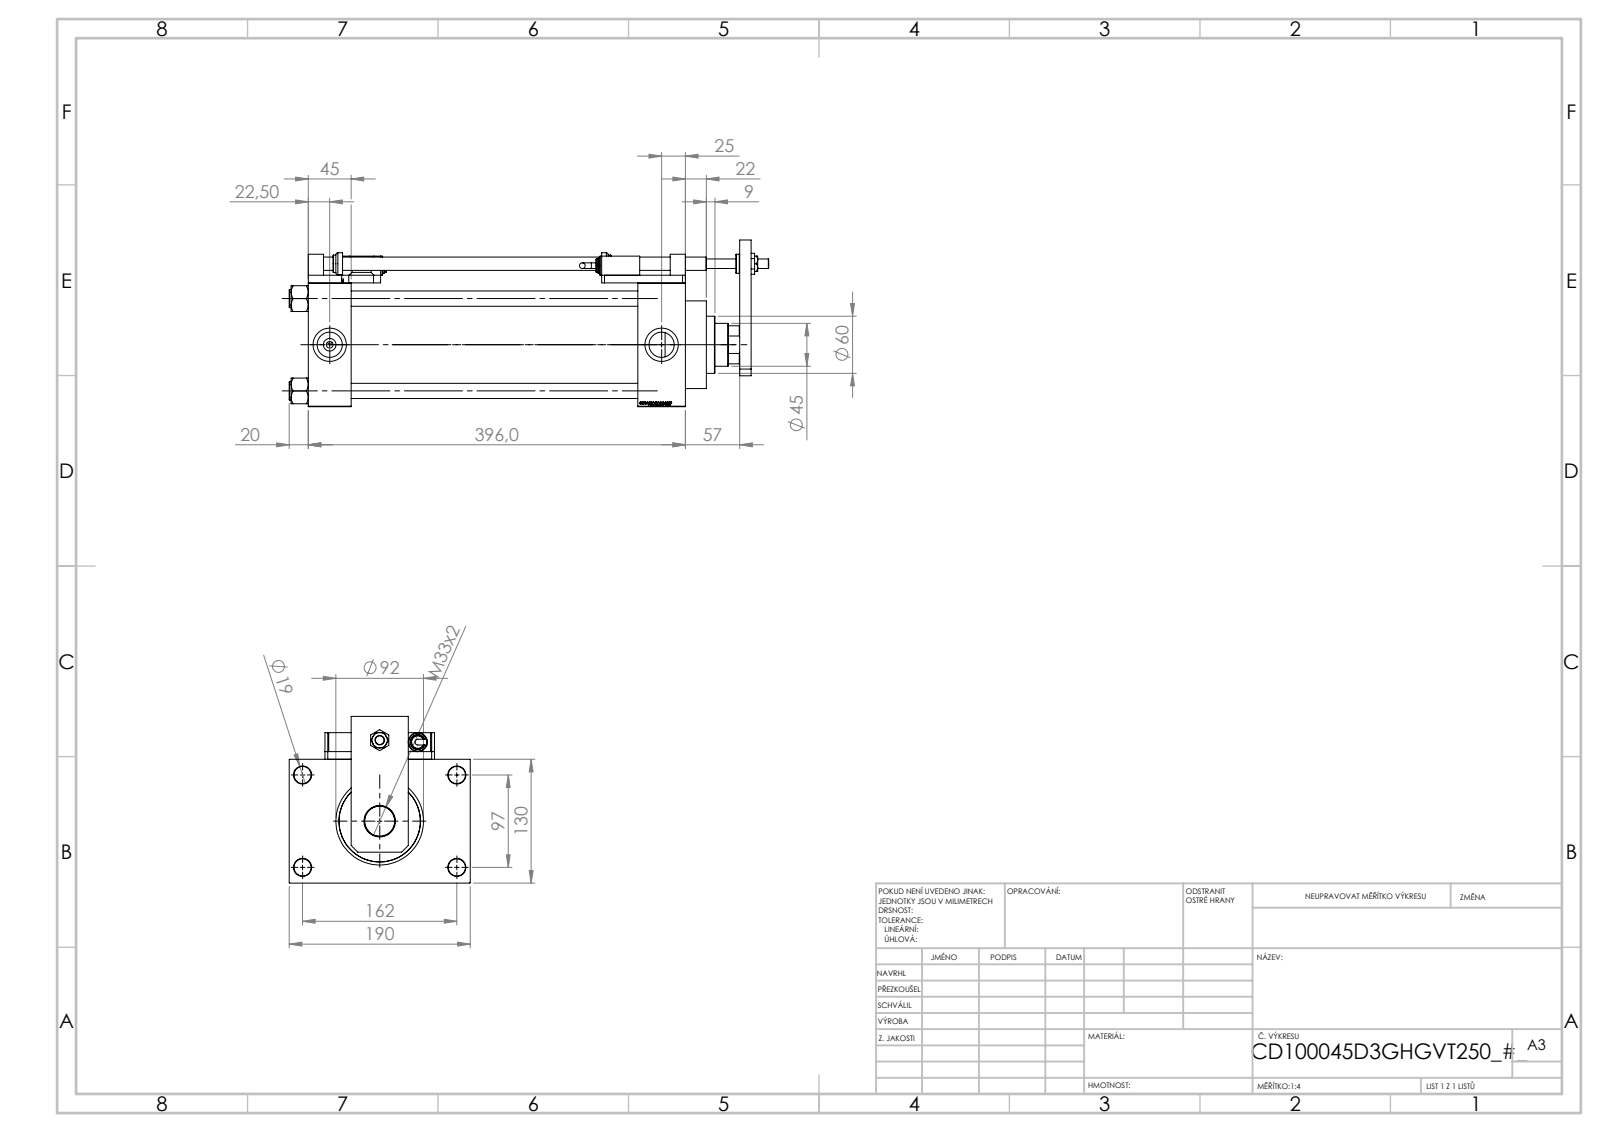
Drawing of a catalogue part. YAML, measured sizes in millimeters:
part_name: "V215CD_SWITCH_Q_SWITCH; V215CD_VC_A; V215CD_NUT_M5_D; Zatka_pro_OIL_PORT (+8 more)"
step_written_by: "SolidWorks 2019 (CONFIG_CONTROL_DESIGN)"
units: millimeters
bodies: {solids: 26, faces: 1480, planar: 714, cylindrical: 167, other: 599}
overall_size: [503.5, 190, 175]
volume: 3715000
surface_area: 696735
round_holes:
  - {diameter: 8.5, count: 4}
  - {diameter: 13.5, count: 4}
  - {diameter: 16, count: 4}
  - {diameter: 18, count: 4}
  - {diameter: 26.44, count: 4}
  - {diameter: 35, count: 4}
  - {diameter: 7, count: 3}
  - {diameter: 10, count: 1}
  - {diameter: 14, count: 1}
  - {diameter: 31.5, count: 1}
  - {diameter: 33, count: 1}
  - {diameter: 45, count: 1}
round_bosses_or_shafts:
  - {diameter: 19, count: 4}
  - {diameter: 20, count: 3}
  - {diameter: 16, count: 2}
  - {diameter: 14, count: 2}
  - {diameter: 6, count: 2}
  - {diameter: 106, count: 1}
  - {diameter: 92, count: 1}
  - {diameter: 60, count: 1}
partial_cylinders:
  - {radius: 7.5, count: 4}
  - {radius: 22, count: 1}
face_to_face_distances: [45, 130, 351, 396, 8, 50, 346, 301, 138, 30]
hole_center_spacings: [32.55, 68.52, 94.41, 96.9, 102.27, 129.45, 161.73, 21.59]
